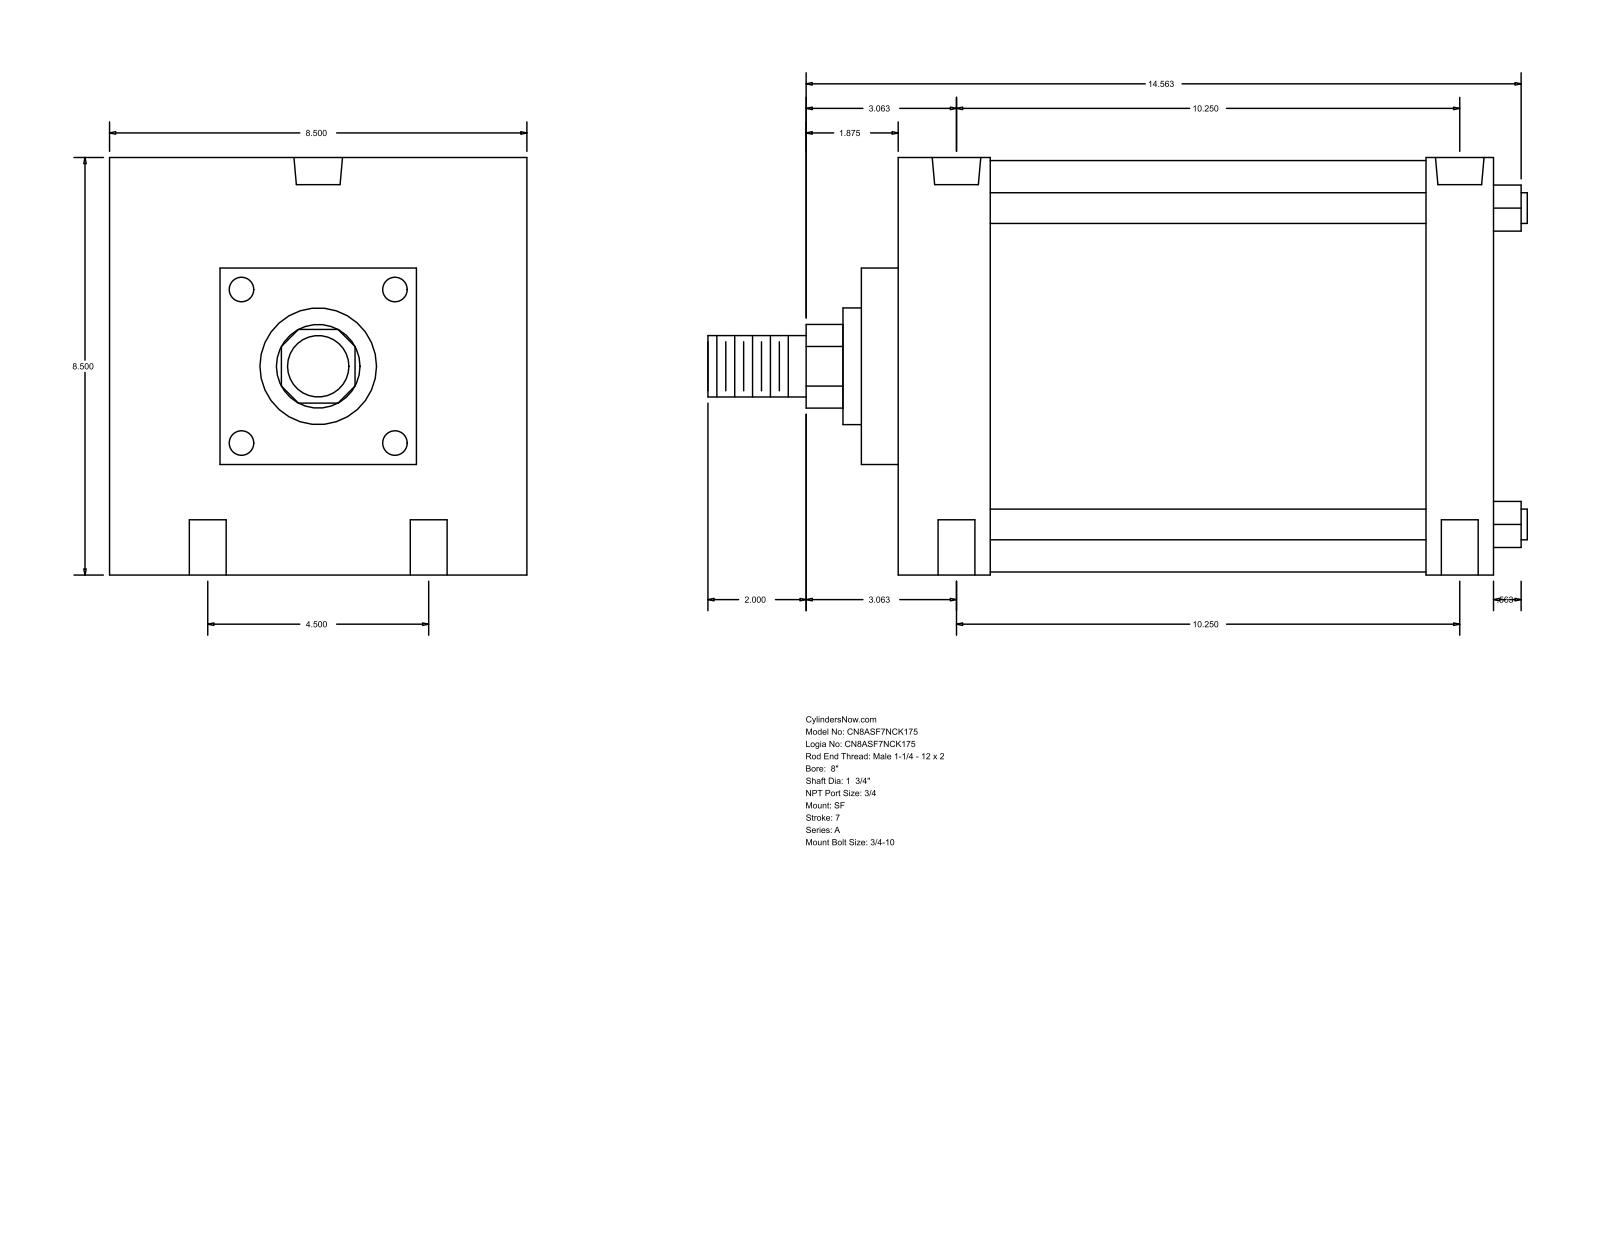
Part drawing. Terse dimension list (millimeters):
name: A_SF__0800_1.75
written by: GSSL Pune (CONFIG_CONTROL_DESIGN)
unit: mm
bodies: 0 solids, 93 faces (67 planar, 26 cylindrical, 0 other)
size: 423.86 × 215.9 × 215.9
holes: 4× ⌀19.05, 2× ⌀15.08, 2× ⌀25.12
bosses: 4× ⌀15.88, 1× ⌀212.72, 1× ⌀60.33, 1× ⌀44.45, 1× ⌀31.75
rounds: 1× R21.63
face distances: 307.98, 215.9, 47.63, 273.06, 225.43, 260.35, 34.92, 19.05, 158.75, 57.15
hole spacings: 57.15, 266.55, 260.35, 114.3, 284.34, 247.65
